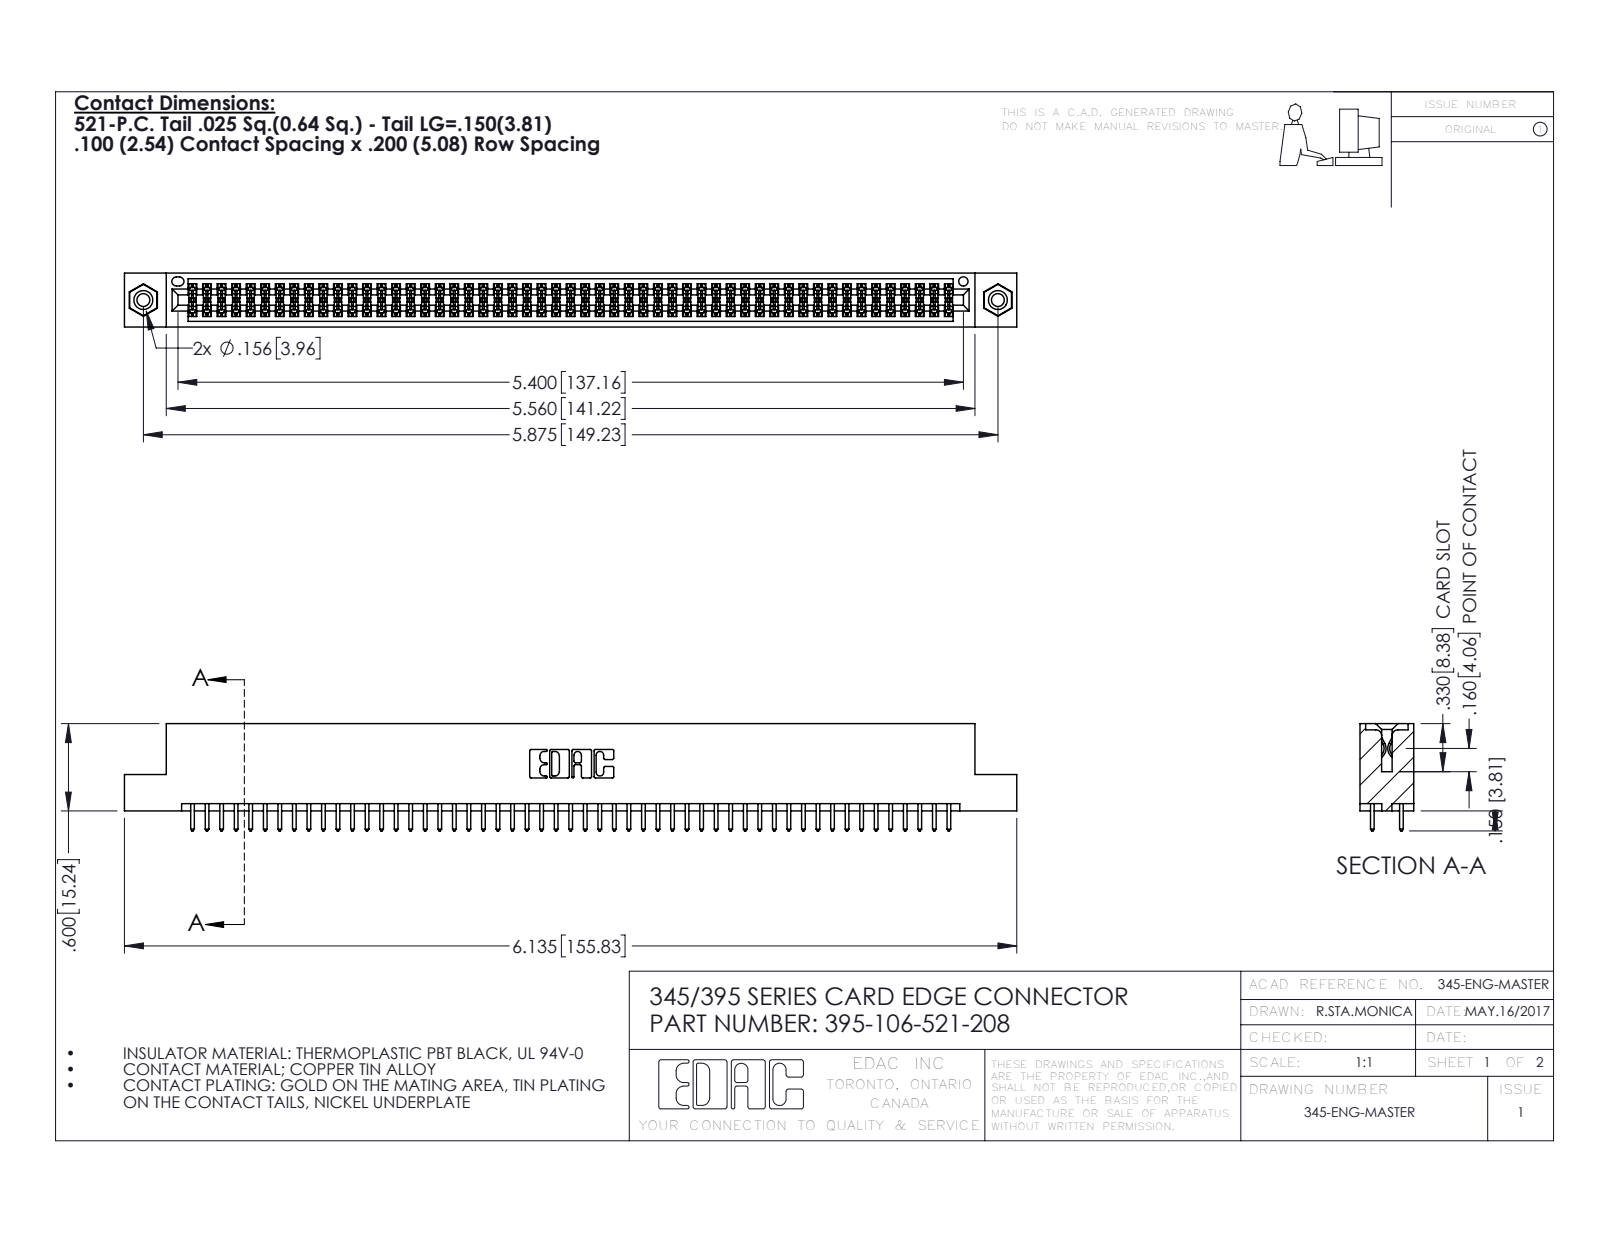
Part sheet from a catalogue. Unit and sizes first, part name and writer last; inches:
Units: inches
Overall size (bounding box): 6.135 × 0.737 × 0.37
Round holes (diameter × count): ⌀0.089 ×2, ⌀0.125 ×2, ⌀0.156 ×2, ⌀0.064 ×1
Round bosses / shafts (diameter × count): ⌀0.155 ×2
Partial cylindrical surfaces — rounded edges, fillets, slot ends (radius × count): R0.006 ×159, R0.01 ×106, R0.01 ×22, R0.007 ×6, R0.031 ×6, R0.026 ×3, R0.014 ×2, R0.019 ×2
Main face-to-face distances: 0.072, 0.298, 0.2, 0.37, 0.098, 0.272, 0.025, 0.225, 0.175, 0.149
Hole centre spacings: 0.27, 5.639, 5.875
Volume: 0.927 in³ · Surface area: 34.72 in²
Bodies: 109 solids, 5486 faces (3610 planar, 1860 cylindrical, 16 other)
Part name (STEP PRODUCT): 345 Part_Flush Mounting Lugs - 0.156 Dia-TI; 345-292-001_345-293-121; 345-250-001_345-250-003-102; 395-106-521-208
STEP written by: SolidWorks 2016 (CONFIG_CONTROL_DESIGN)
